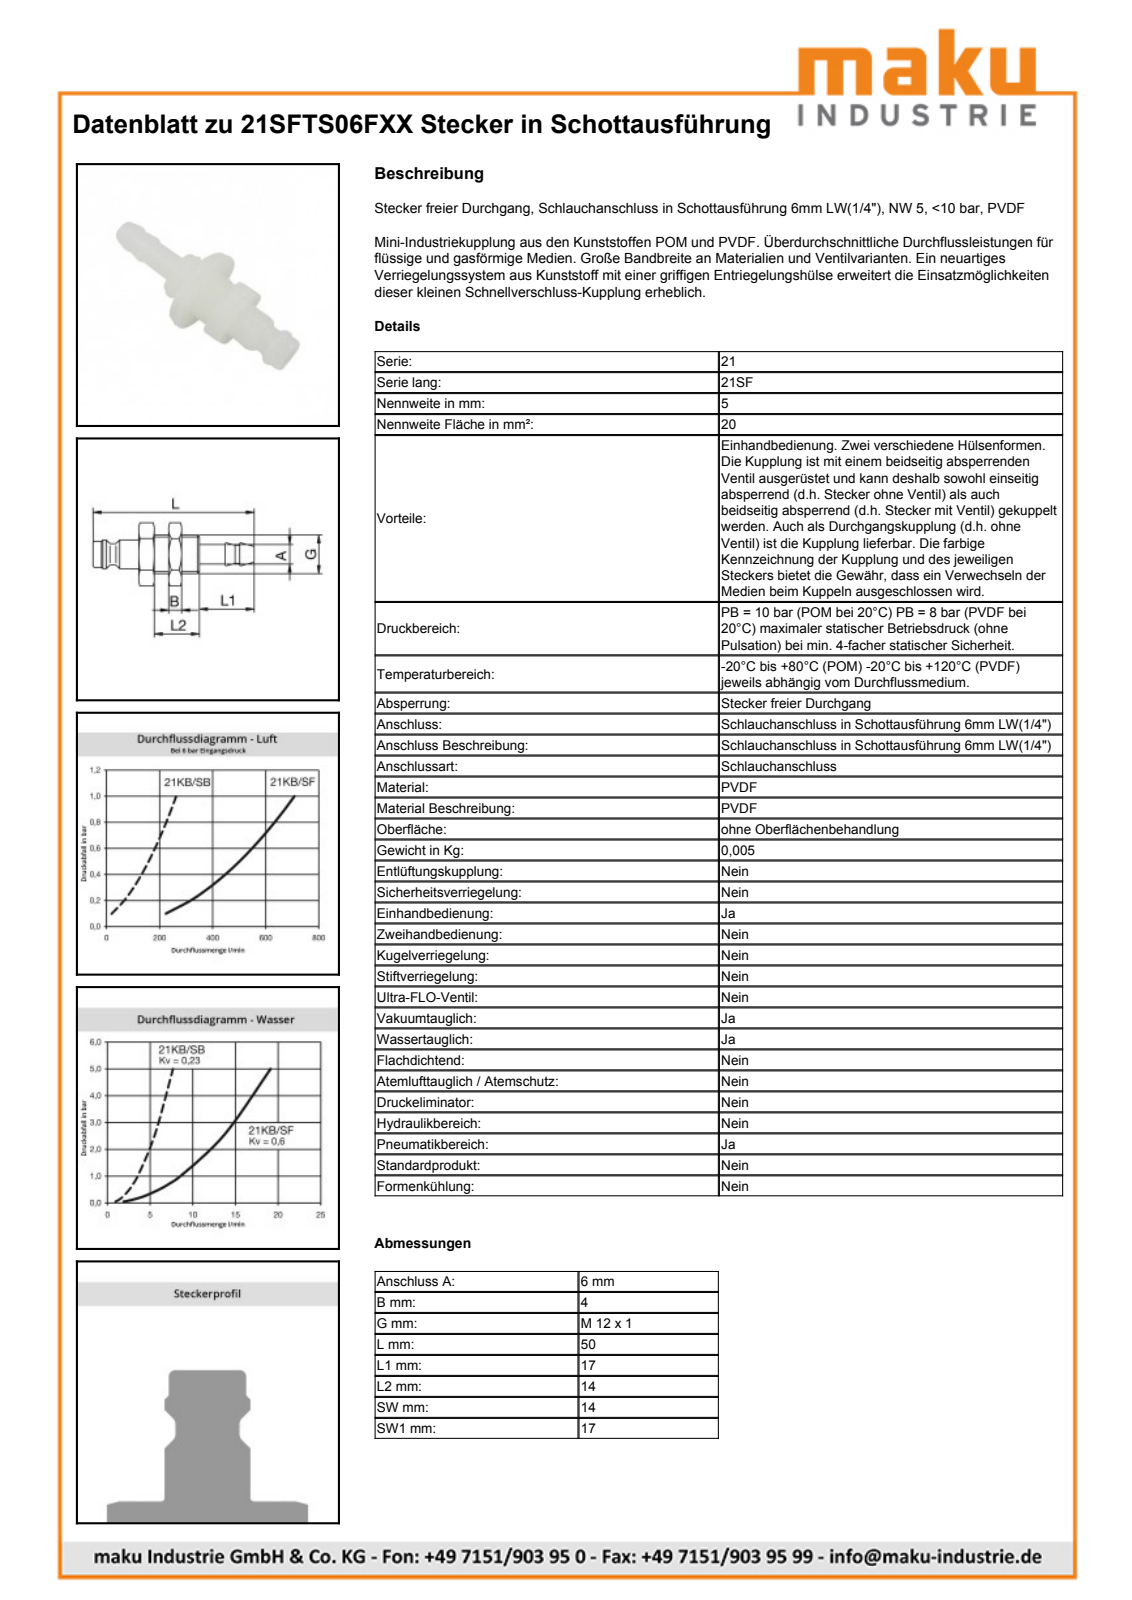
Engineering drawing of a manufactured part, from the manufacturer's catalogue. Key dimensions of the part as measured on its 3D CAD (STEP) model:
Part name (STEP PRODUCT): 21SFTS06FXX; D112646
STEP written by: Autodesk Inventor 2016 (AUTOMOTIVE_DESIGN)
Units: millimetres
Bodies: 2 solids, 261 faces (149 planar, 83 cylindrical, 29 other)
Overall size (bounding box): 50 × 20 × 20
Volume: 3 927 mm³ · Surface area: 3 419 mm²
Round holes (diameter × count): ⌀3.3 ×1, ⌀4.7 ×1, ⌀6.1 ×1, ⌀12 ×1
Round bosses / shafts (diameter × count): ⌀9 ×1, ⌀8.1 ×1, ⌀6.65 ×1, ⌀6.05 ×1, ⌀5.65 ×1
Partial cylindrical surfaces — rounded edges, fillets, slot ends (radius × count): R0.25 ×6, R9.57 ×1, R10 ×1
Main face-to-face distances: 17, 7.66, 4, 11.66, 6.86, 2.86, 4.8, 7.14, 11.14, 14
